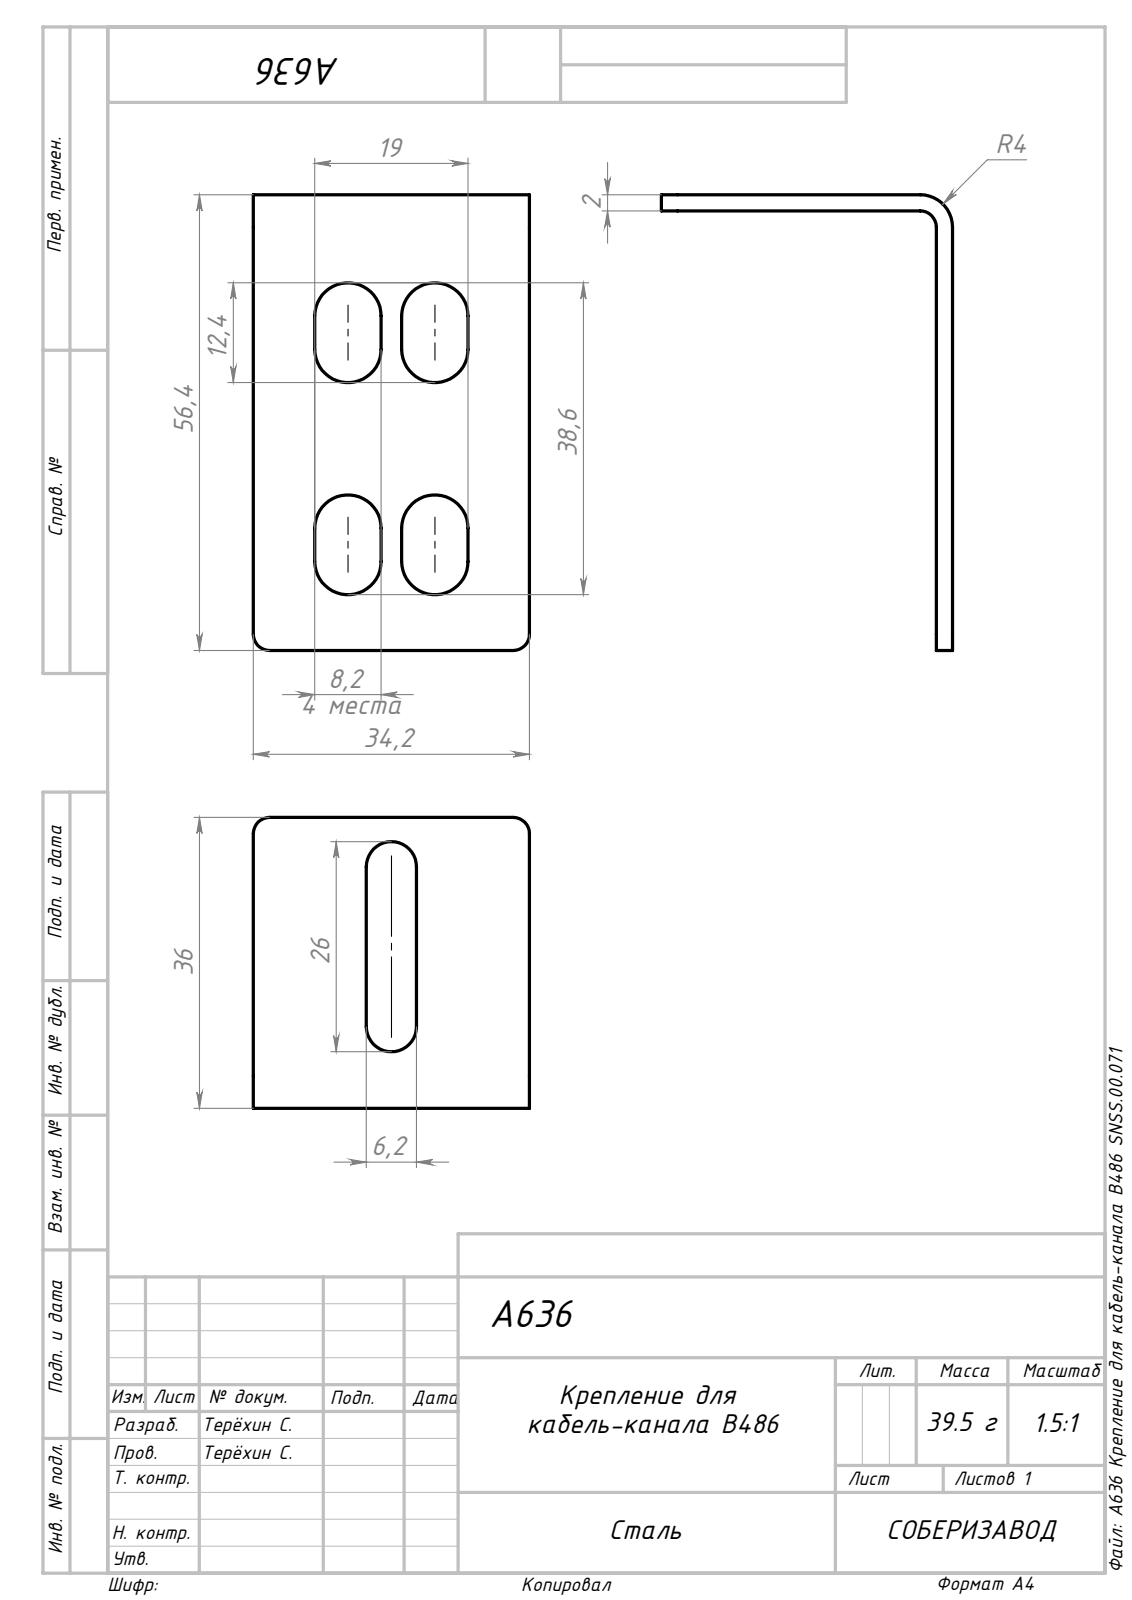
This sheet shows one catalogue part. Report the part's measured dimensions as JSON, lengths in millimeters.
{"part_name": "Сборка2; A636 Крепление для кабель-канала B486 SNSS.00.071_1", "step_written_by": "SolidWorks 2022 (AUTOMOTIVE_DESIGN)", "units": "millimeters", "bodies": {"solids": 1, "faces": 43, "planar": 22, "cylindrical": 21, "other": 0}, "overall_size": [56.4, 36, 34.15], "volume_mm3": 5079, "surface_area_mm2": 5956, "partial_cylinders_radius": [[4.1, 8], [2, 5], [3.1, 2], [4, 1]], "face_to_face_distances": [2, 34.15, 34, 36, 54.4, 56.4, 20.18, 13.97, 13.98, 6.2]}
